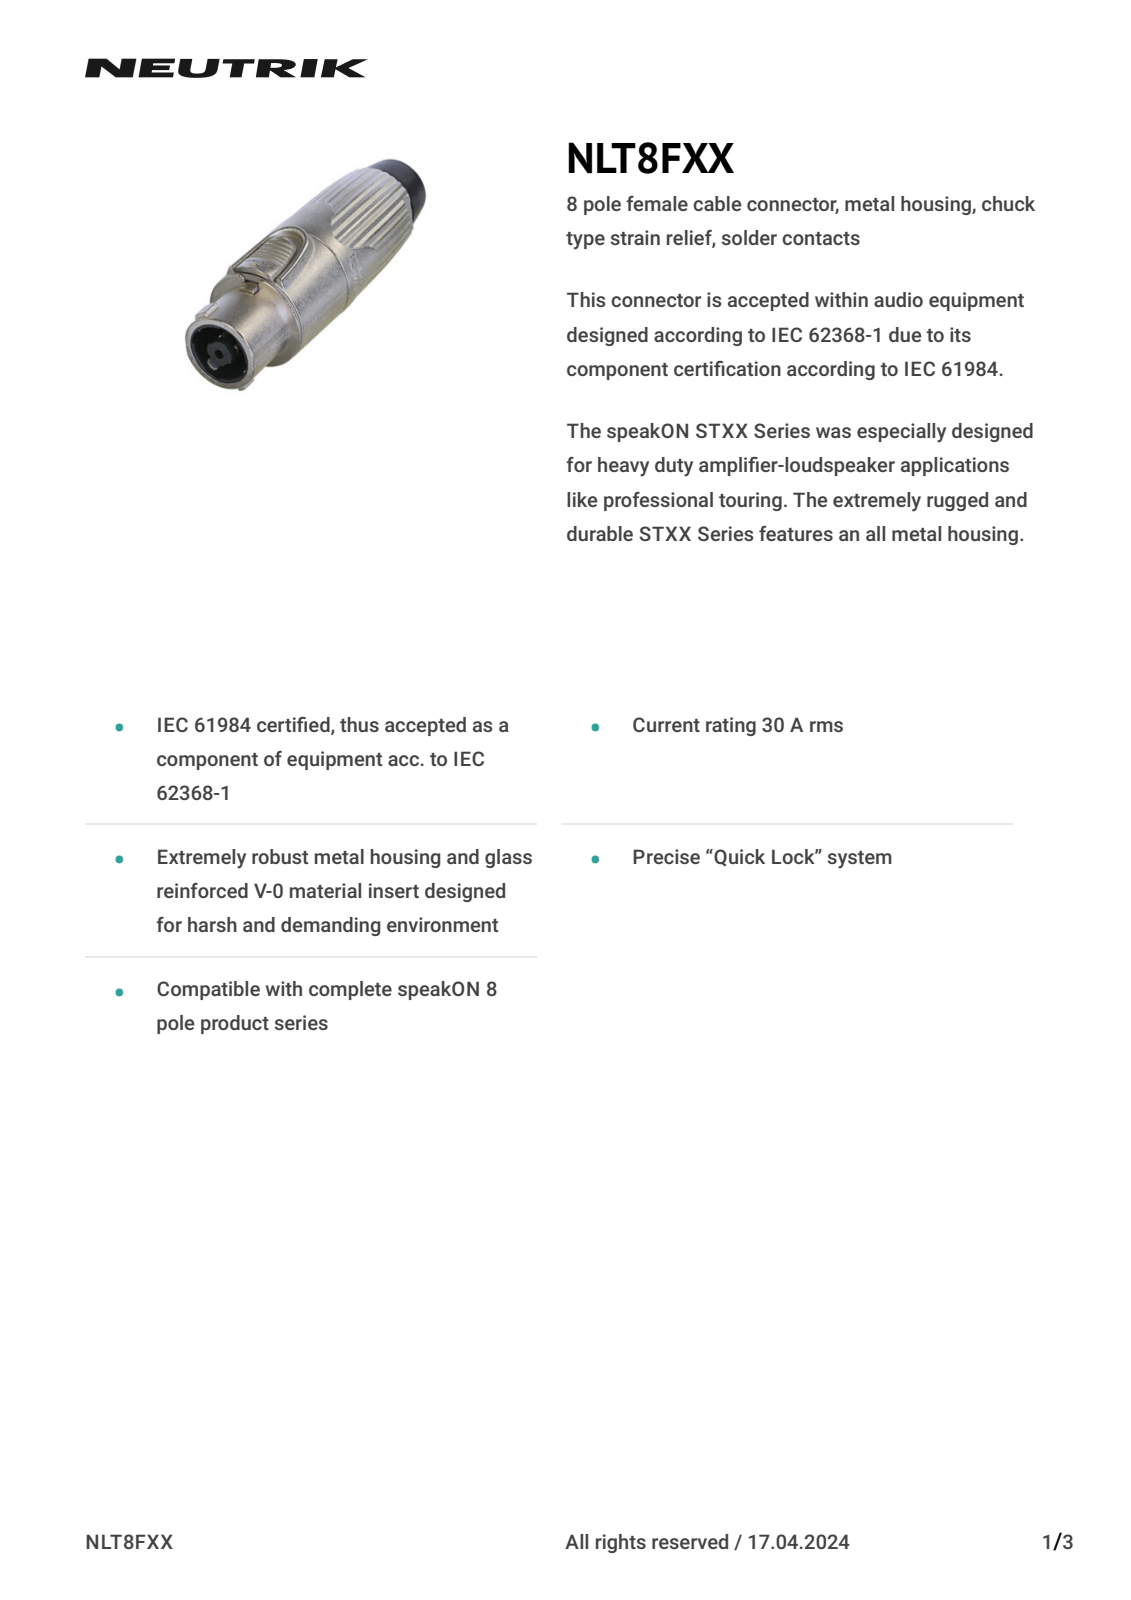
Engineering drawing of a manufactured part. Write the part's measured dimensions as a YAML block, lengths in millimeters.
part_name: "NLT8FXX"
step_written_by: "CREO PARAMETRIC BY PTC INC, 2019080 (CONFIG_CONTROL_DESIGN)"
units: millimeters
bodies: {solids: 1, faces: 2355, planar: 1374, cylindrical: 208, other: 773}
overall_size: [116.91, 35.31, 35.31]
volume: 83791
surface_area: 19286
round_holes:
  - {diameter: 7, count: 1}
  - {diameter: 20.6, count: 1}
round_bosses_or_shafts:
  - {diameter: 32.3, count: 1}
  - {diameter: 27, count: 1}
  - {diameter: 20.4, count: 1}
partial_cylinders:
  - {radius: 0.2, count: 41}
  - {radius: 0.5, count: 28}
  - {radius: 0.7, count: 28}
  - {radius: 10, count: 5}
  - {radius: 0.9, count: 4}
  - {radius: 1, count: 4}
  - {radius: 7, count: 4}
  - {radius: 0.1, count: 2}
face_to_face_distances: [96.81, 0.8, 0.9, 116.91, 20.1, 95.91, 21, 1.5, 0.7, 18.02]
